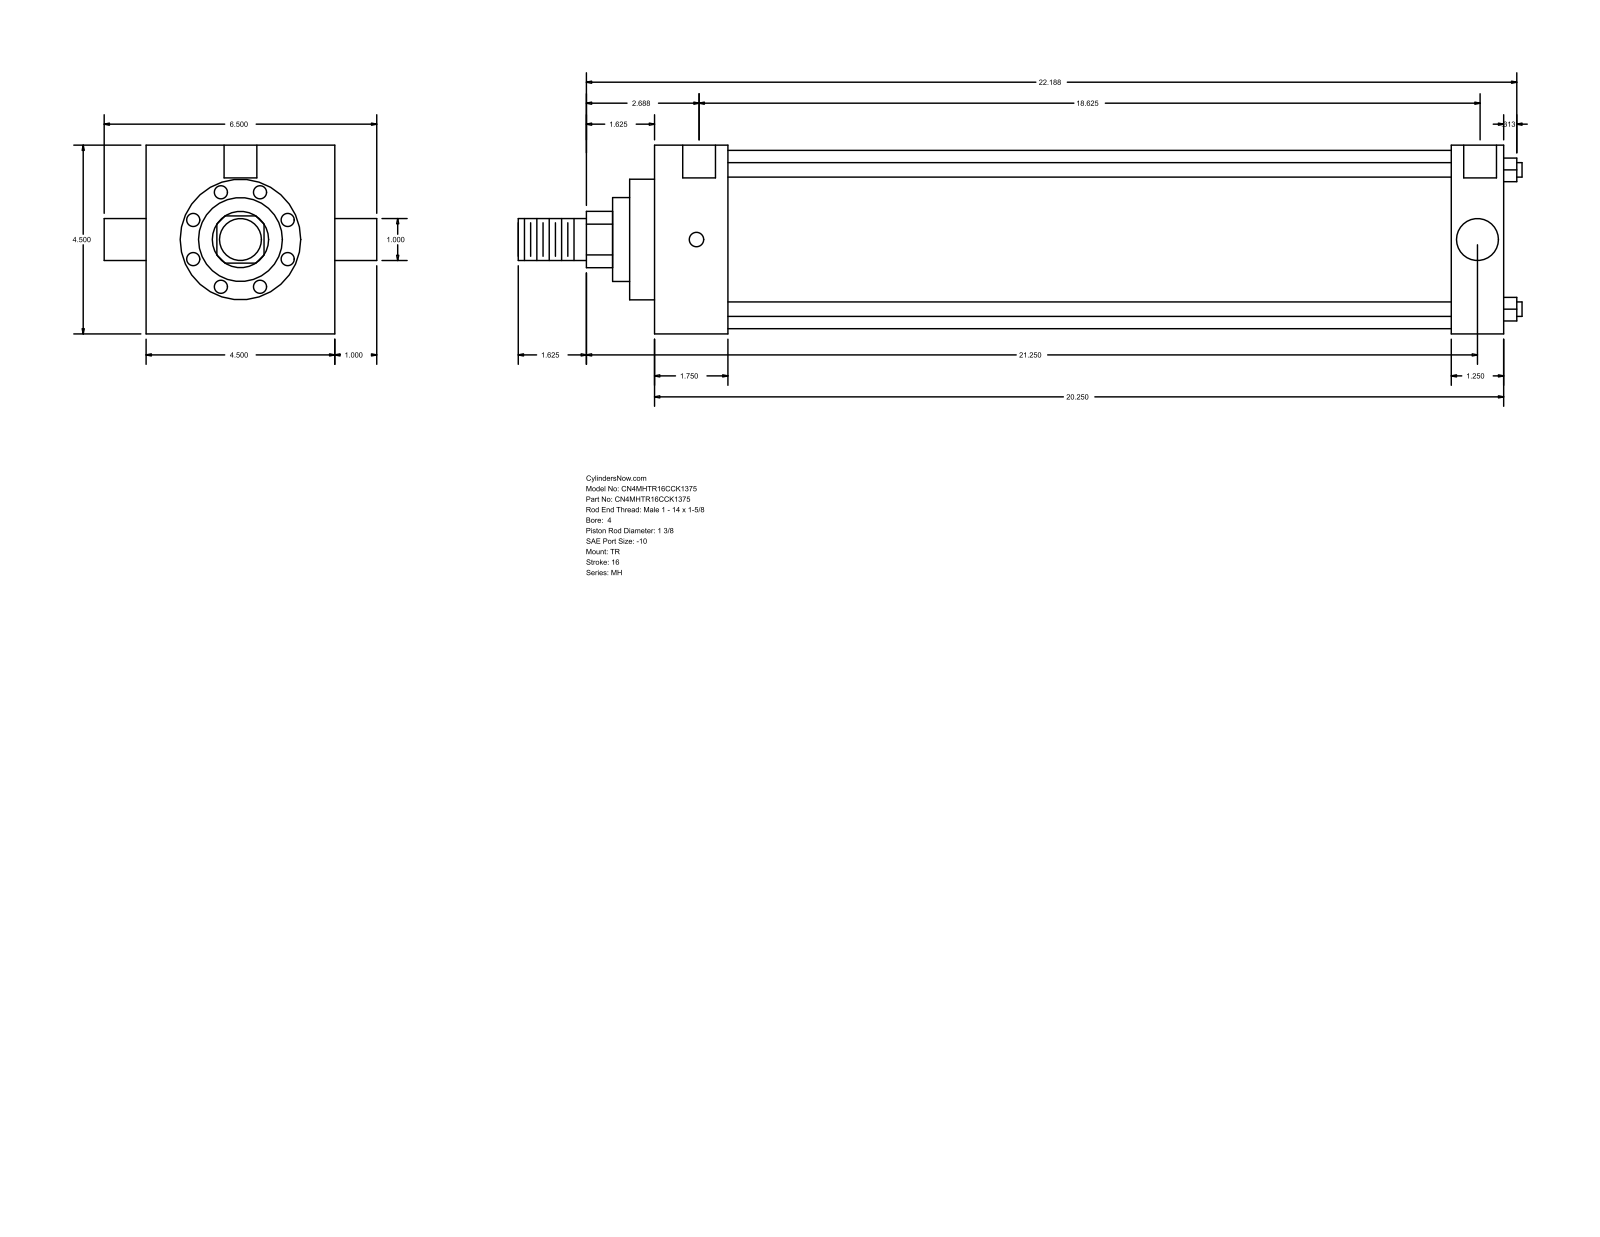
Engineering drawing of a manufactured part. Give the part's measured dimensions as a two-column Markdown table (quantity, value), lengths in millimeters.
| quantity | value |
| --- | --- |
| part name | MH_TR__0400_1.375 |
| STEP written by | GSSL Pune (CONFIG_CONTROL_DESIGN) |
| units | millimeters |
| bodies | 0 solids, 86 faces (61 planar, 25 cylindrical, 0 other) |
| overall size | 608.01 × 165.1 × 114.3 |
| round holes (diameter × count) | 8.73 × 3, 19.84 × 2 |
| round bosses / shafts (diameter × count) | 8.76 × 4, 25.4 × 2, 107.95 × 1, 73.03 × 1, 50.8 × 1, 34.92 × 1 |
| partial cylindrical surfaces (radius × count) | 17.06 × 1 |
| main face-to-face distances | 114.3, 514.35, 44.45, 469.9, 482.61, 438.16, 31.74, 15.08, 59.53, 497.69 |
| hole center spacings | 1.58, 1.59, 473.08, 474.66, 474.67, 476.25 |
